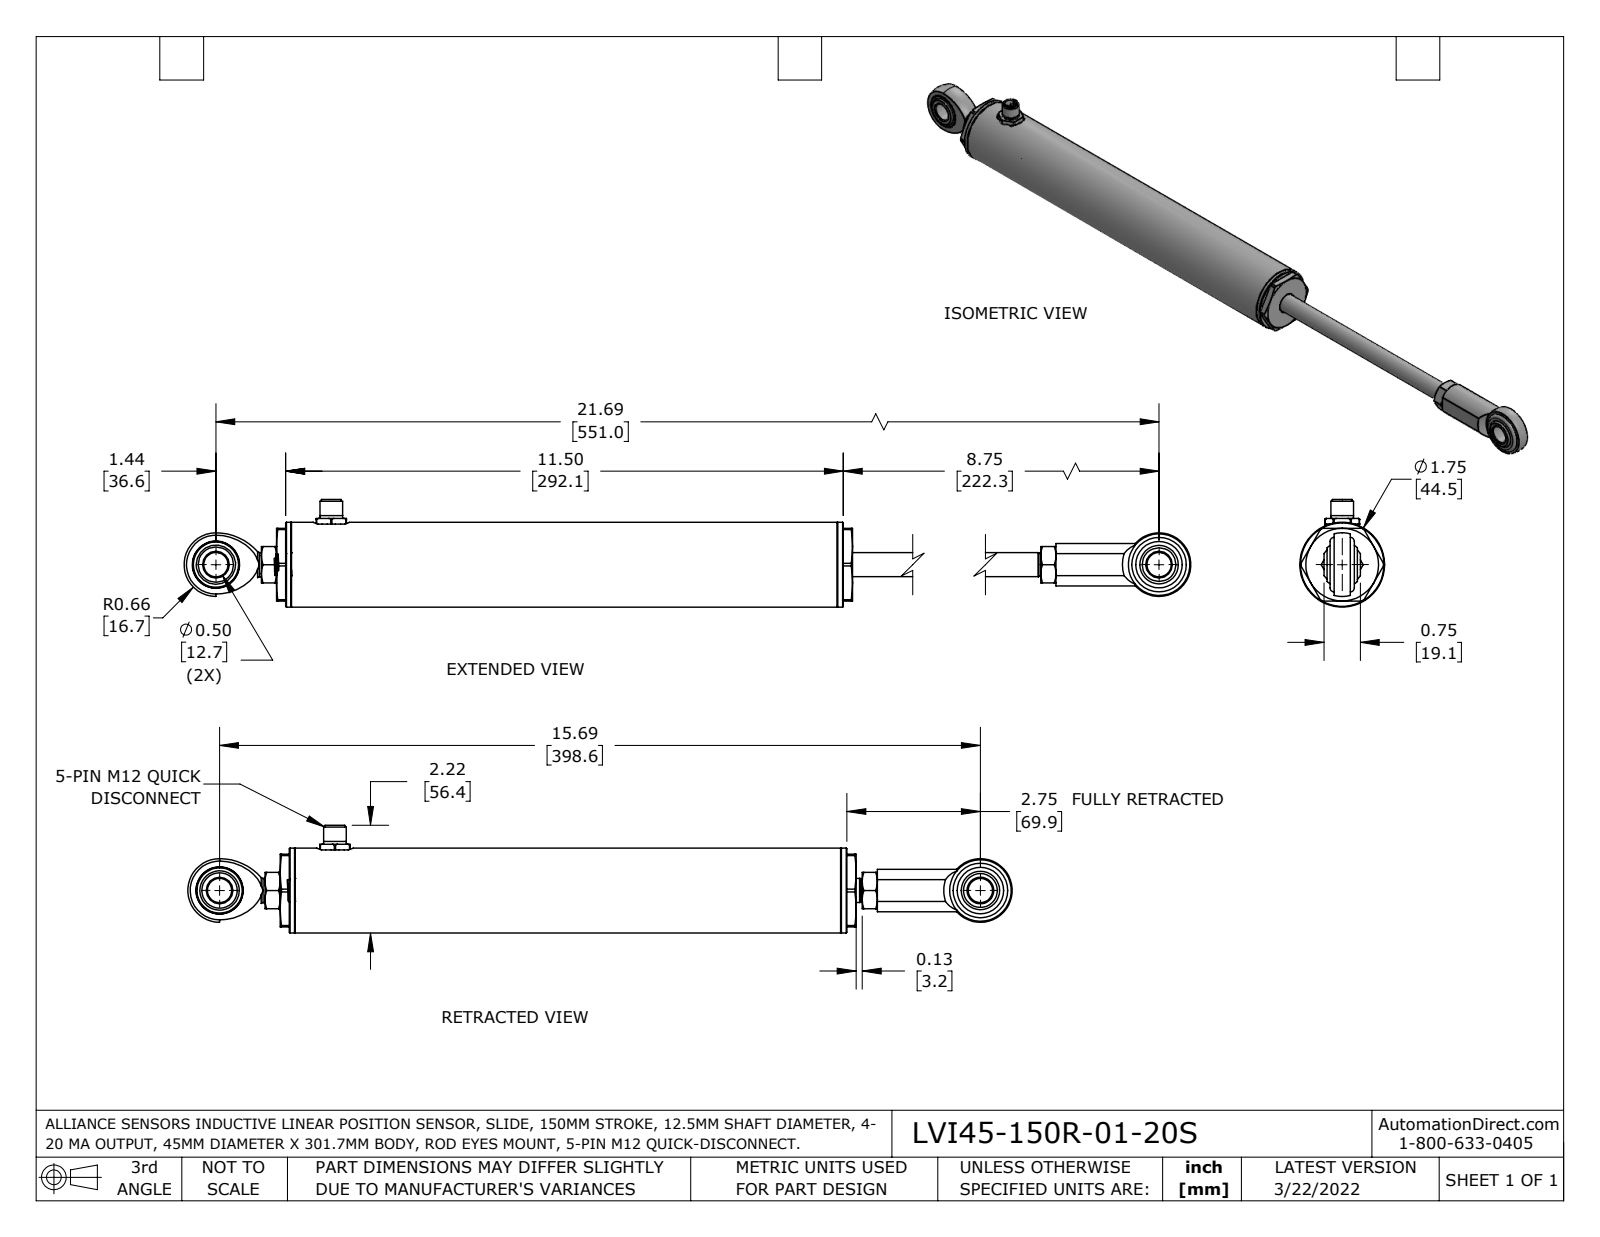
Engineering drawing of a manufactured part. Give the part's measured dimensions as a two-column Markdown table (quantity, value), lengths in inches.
| quantity | value |
| --- | --- |
| part name | 3900-0008-XX-Y_-06; 3100-0212; 3100-0020; 3100-0012-YY (+8 more) |
| STEP written by | SolidWorks 2021 (AUTOMOTIVE_DESIGN) |
| units | inches |
| bodies | 23 solids, 873 faces (198 planar, 297 cylindrical, 378 other) |
| overall size | 23.004 × 2.219 × 1.75 |
| volume | 15.76 in³ |
| surface area | 229.1 in² |
| round holes (diameter × count) | 0.501 × 3, 0.197 × 1, 0.25 × 1, 0.264 × 1, 0.309 × 1, 0.329 × 1, 0.339 × 1, 0.413 × 1, 0.417 × 1, 0.453 × 1, 0.478 × 1, 0.5 × 1 |
| round bosses / shafts (diameter × count) | 0.031 × 5, 1.75 × 1, 1.625 × 1, 1.562 × 1, 1.531 × 1, 1.5 × 1, 1.47 × 1, 1.384 × 1 |
| partial cylindrical surfaces (radius × count) | 0.325 × 1, 0.354 × 1, 0.378 × 1, 0.38 × 1, 0.438 × 1, 0.85 × 1 |
| main face-to-face distances | 1.93, 0.5, 0.38, 0.69, 2.62, 9.573, 2.24, 1.55, 9.763, 9.073 |
| hole center spacings | 0.5, 21.693 |
